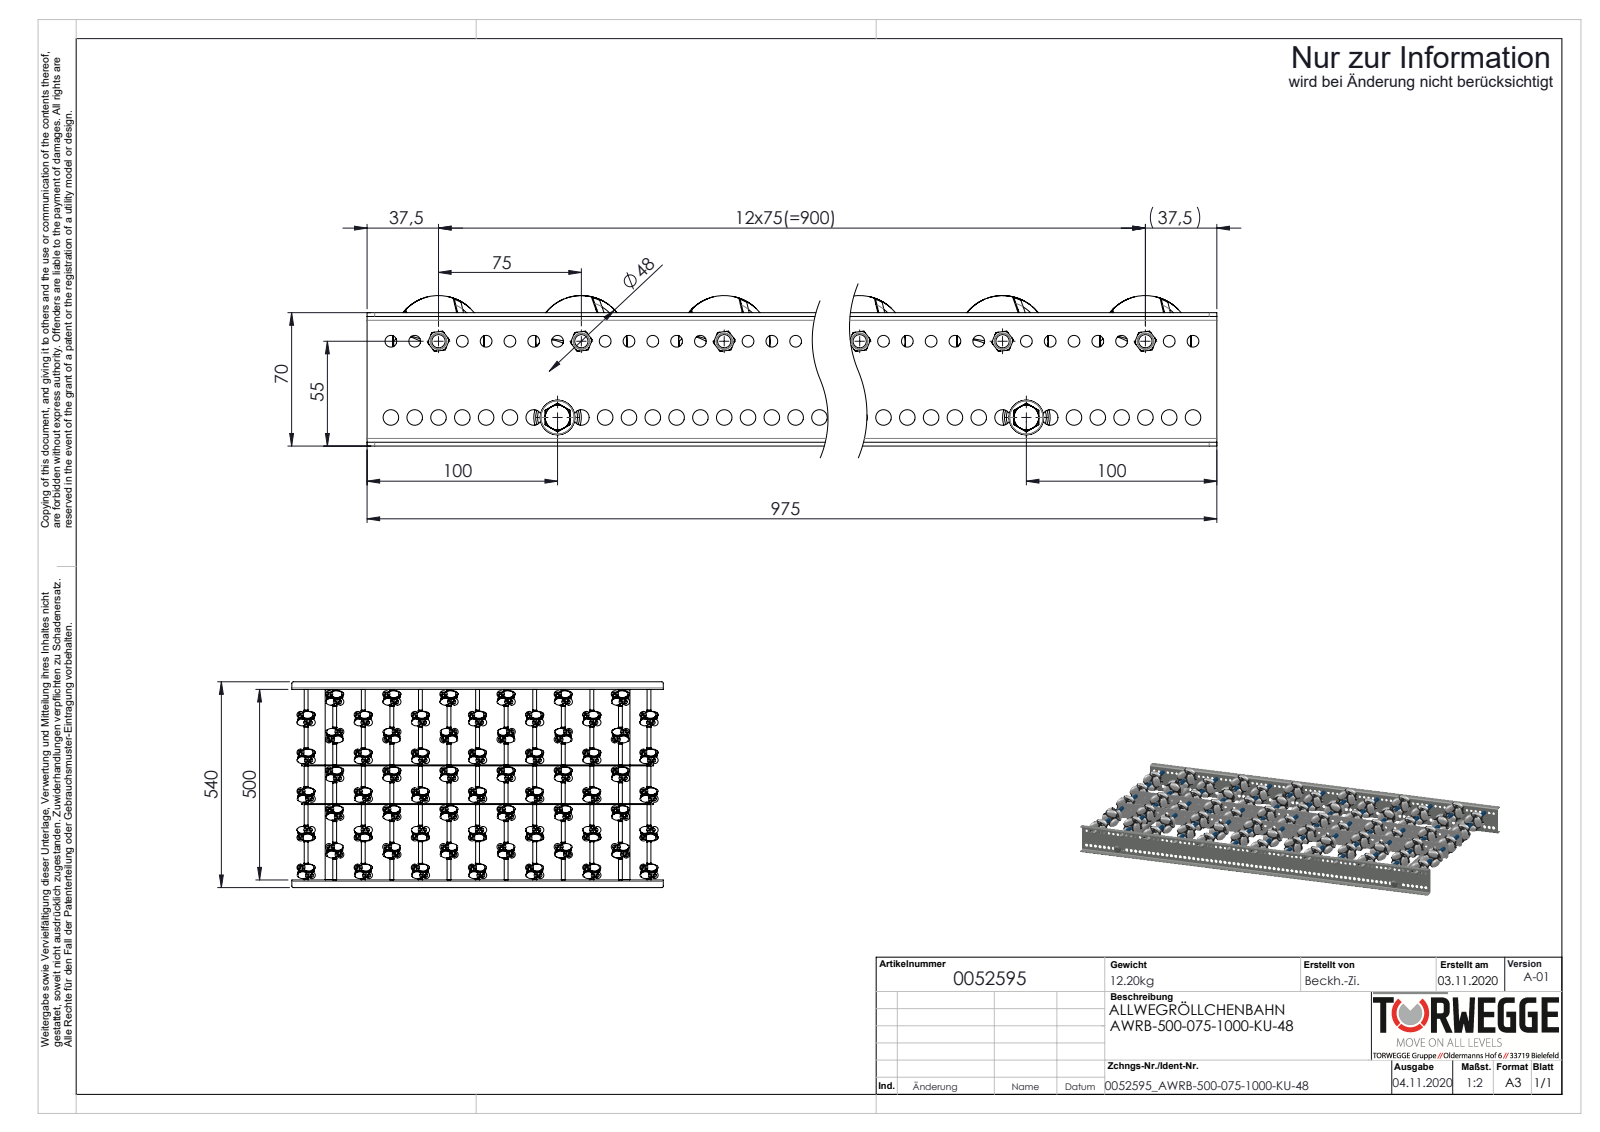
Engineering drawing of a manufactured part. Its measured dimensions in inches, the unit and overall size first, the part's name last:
Units: inches
Overall size (bounding box): 38.386 × 21.26 × 3.11
Round holes (diameter × count): ⌀0.146 ×390, ⌀0.165 ×390, ⌀0.244 ×77, ⌀0.323 ×77, ⌀0.256 ×37, ⌀0.194 ×13, ⌀0.331 ×13, ⌀0.268 ×2, ⌀0.827 ×2
Round bosses / shafts (diameter × count): ⌀0.157 ×390, ⌀0.146 ×346, ⌀0.315 ×15, ⌀1.654 ×13, ⌀0.433 ×13, ⌀0.394 ×13, ⌀0.276 ×13, ⌀0.236 ×13
Partial cylindrical surfaces — rounded edges, fillets, slot ends (radius × count): R0.927 ×13, R0.157 ×8, R0.079 ×4, R0.197 ×4
Main face-to-face distances: 0.079, 19.764, 3.996, 0.098, 2.677, 19.685, 19.843, 3.898, 4.094, 7.878
Hole centre spacings: 1.42, 1.419, 1.42, 5.906, 2.953, 1.419, 1.83, 1.954
Volume: 235.5 in³ · Surface area: 4 163 in²
Bodies: 1093 solids, 19602 faces (6736 planar, 7718 cylindrical, 5148 other)
Part name (STEP PRODUCT): 0019730_Tragrollenrohr-Ø10x1,75KU_KFG_0019730_L=54; AWR48_Halter; S100994_Sperrzahnschraube_M08x16-8.8-A2K; Traversen_KFG_L500 (+8 more)
STEP written by: SolidWorks 2020 (AUTOMOTIVE_DESIGN)
